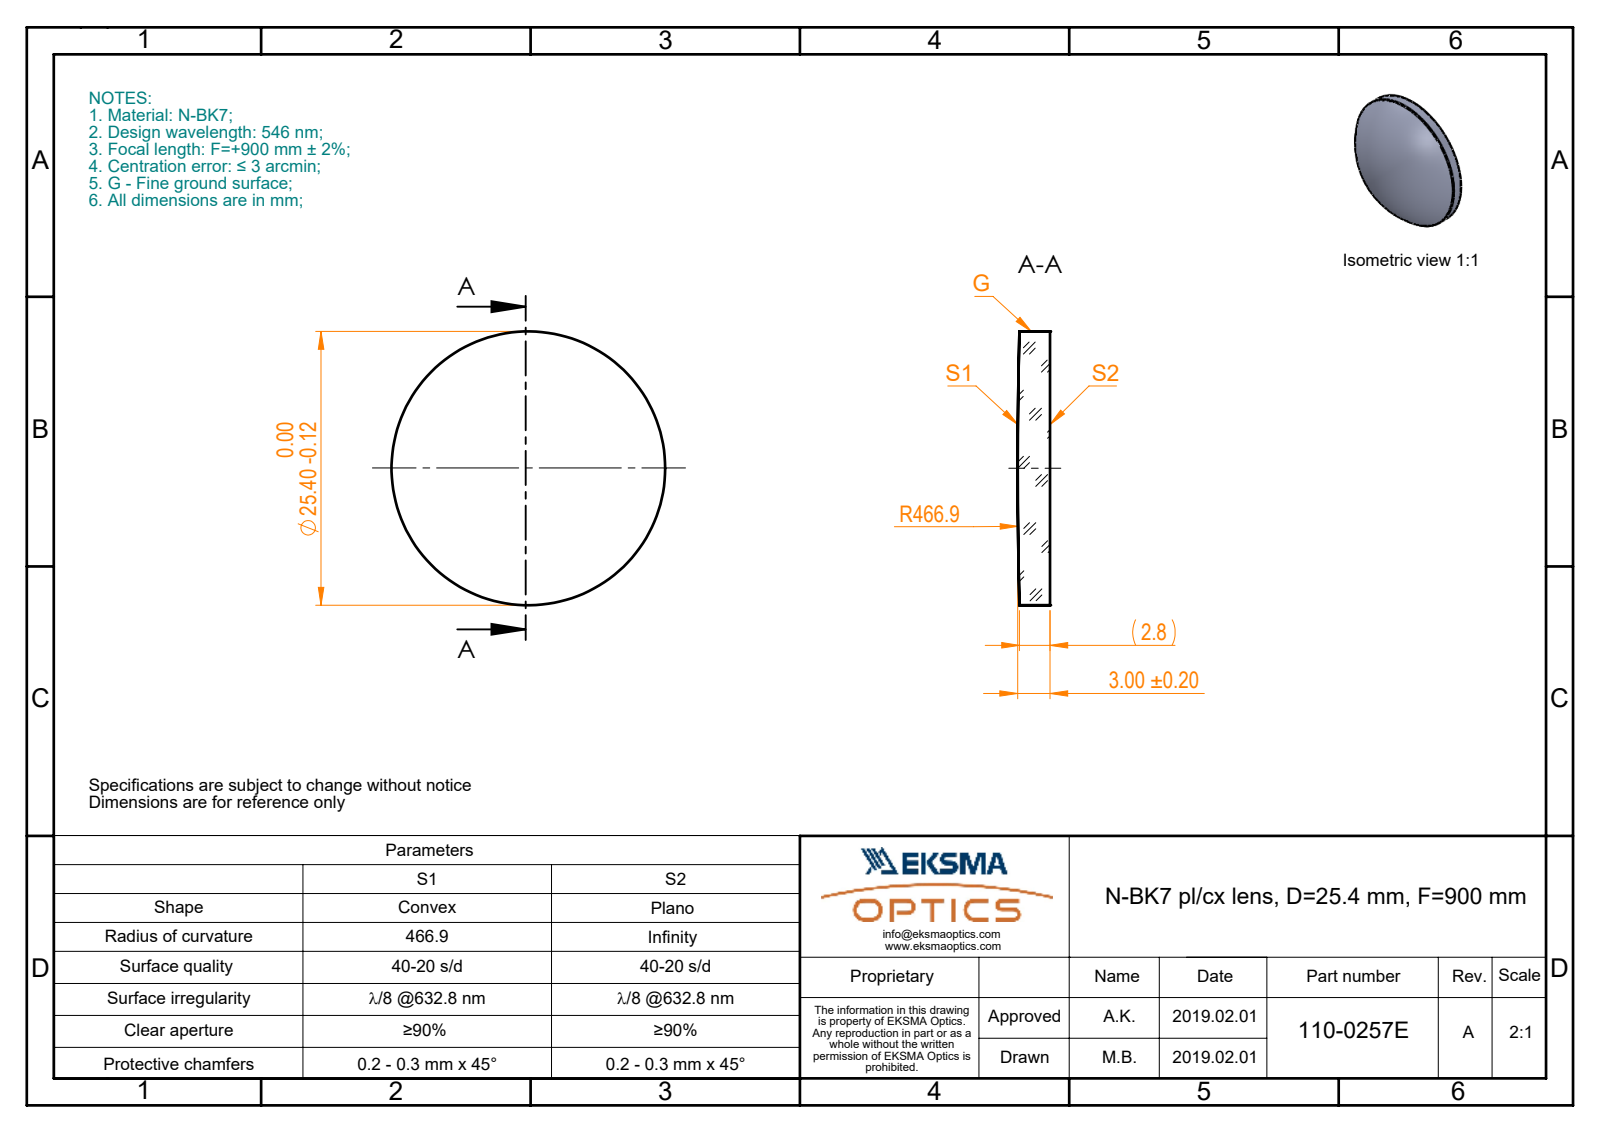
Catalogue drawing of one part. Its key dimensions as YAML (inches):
part_name: "110-0257E BK7 pl-cx 25.4 F900"
step_written_by: "SolidWorks 2017 (CONFIG_CONTROL_DESIGN)"
units: inches
bodies: {solids: 1, faces: 5, planar: 1, cylindrical: 2, other: 2}
overall_size: [1, 1, 0.118]
volume: 0.09
surface_area: 1.92
round_bosses_or_shafts:
  - {diameter: 1, count: 1}
